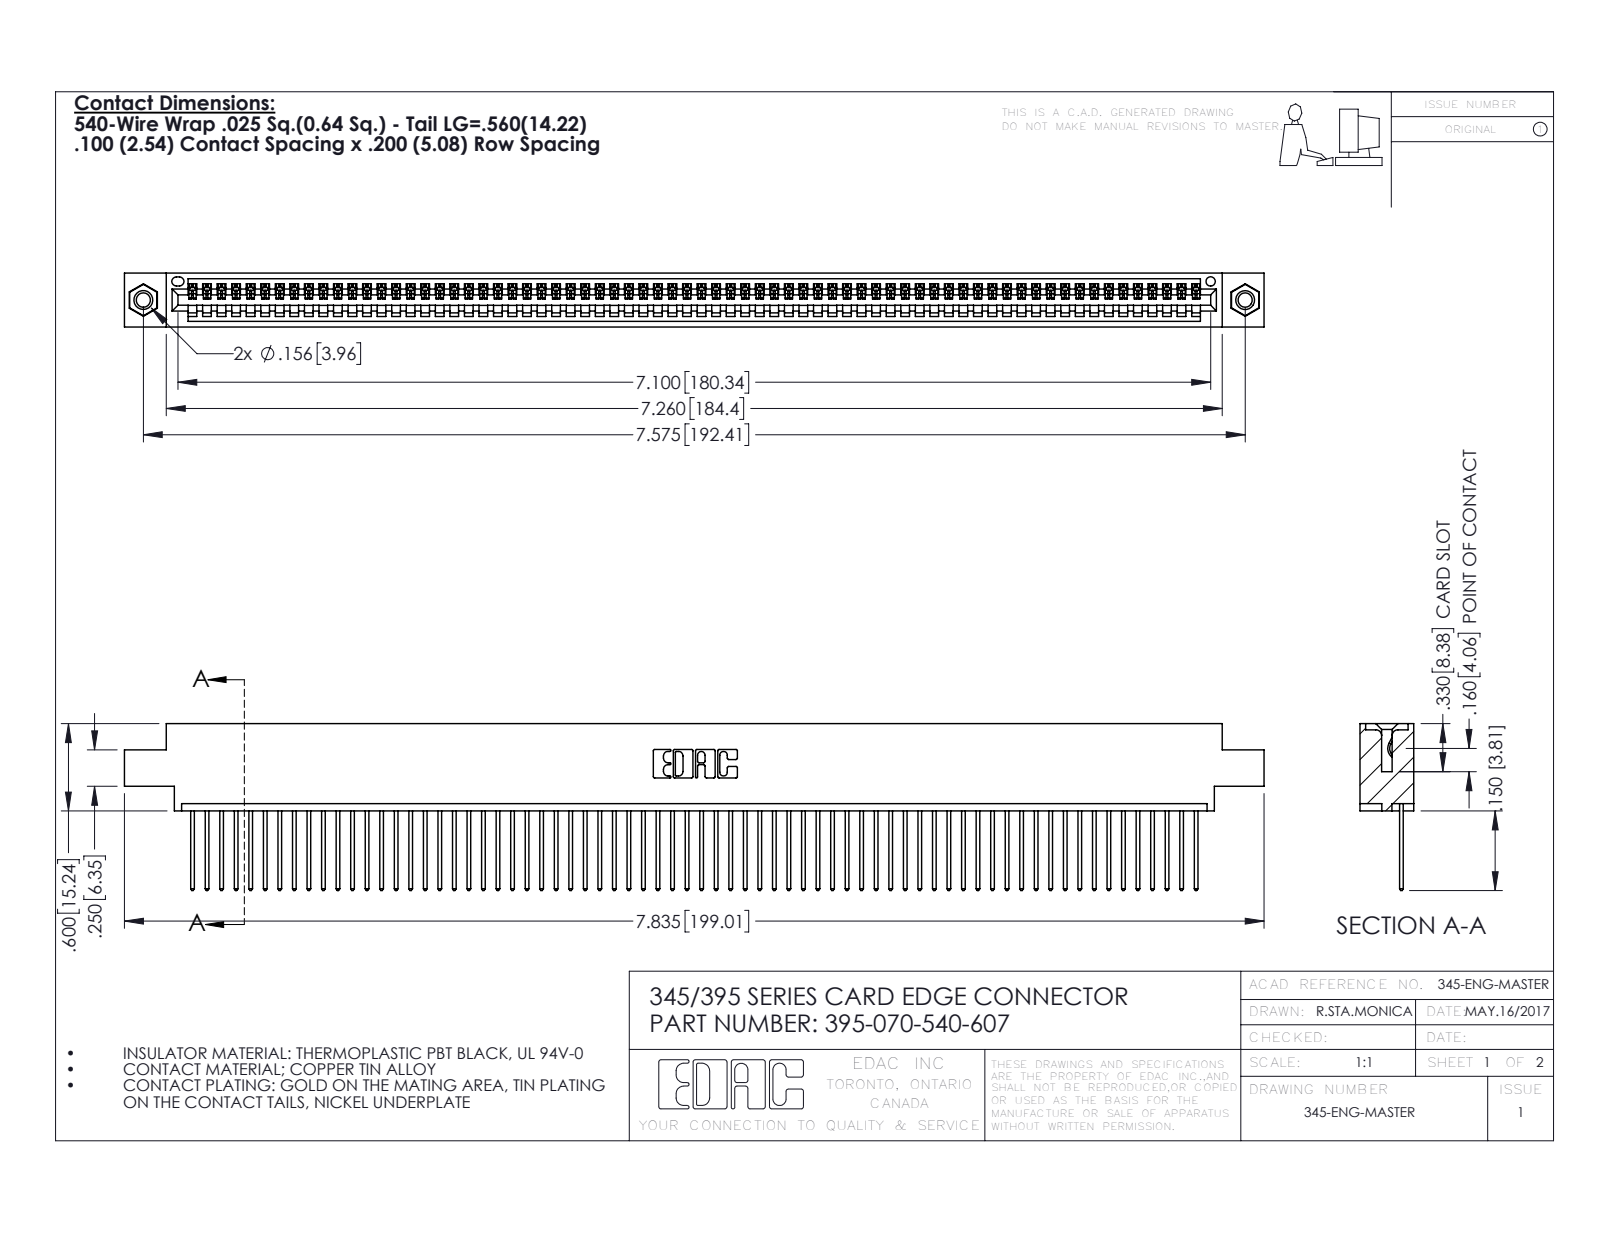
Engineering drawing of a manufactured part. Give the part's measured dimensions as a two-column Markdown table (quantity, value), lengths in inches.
| quantity | value |
| --- | --- |
| part name | 345 Part_0.170 Offset - 0.156 Dia-TI; 345-250-001_345-250-005-103; 345-292-001_345-293-140; 395-070-540-607 |
| STEP written by | SolidWorks 2016 (CONFIG_CONTROL_DESIGN) |
| units | inches |
| bodies | 73 solids, 4250 faces (2916 planar, 1318 cylindrical, 16 other) |
| overall size | 7.835 × 1.147 × 0.37 |
| volume | 1.166 in³ |
| surface area | 41.23 in² |
| round holes (diameter × count) | 0.098 × 2, 0.125 × 2, 0.156 × 2, 0.064 × 1 |
| round bosses / shafts (diameter × count) | 0.155 × 2 |
| partial cylindrical surfaces (radius × count) | 0.006 × 140, 0.01 × 140, 0.01 × 22, 0.007 × 6, 0.031 × 6, 0.026 × 3, 0.031 × 2, 0.04 × 2 |
| main face-to-face distances | 0.072, 0.298, 0.37, 0.098, 0.272, 0.025, 0.2, 0.225, 0.175, 0.149 |
| hole center spacings | 0.27, 7.339, 7.575 |
